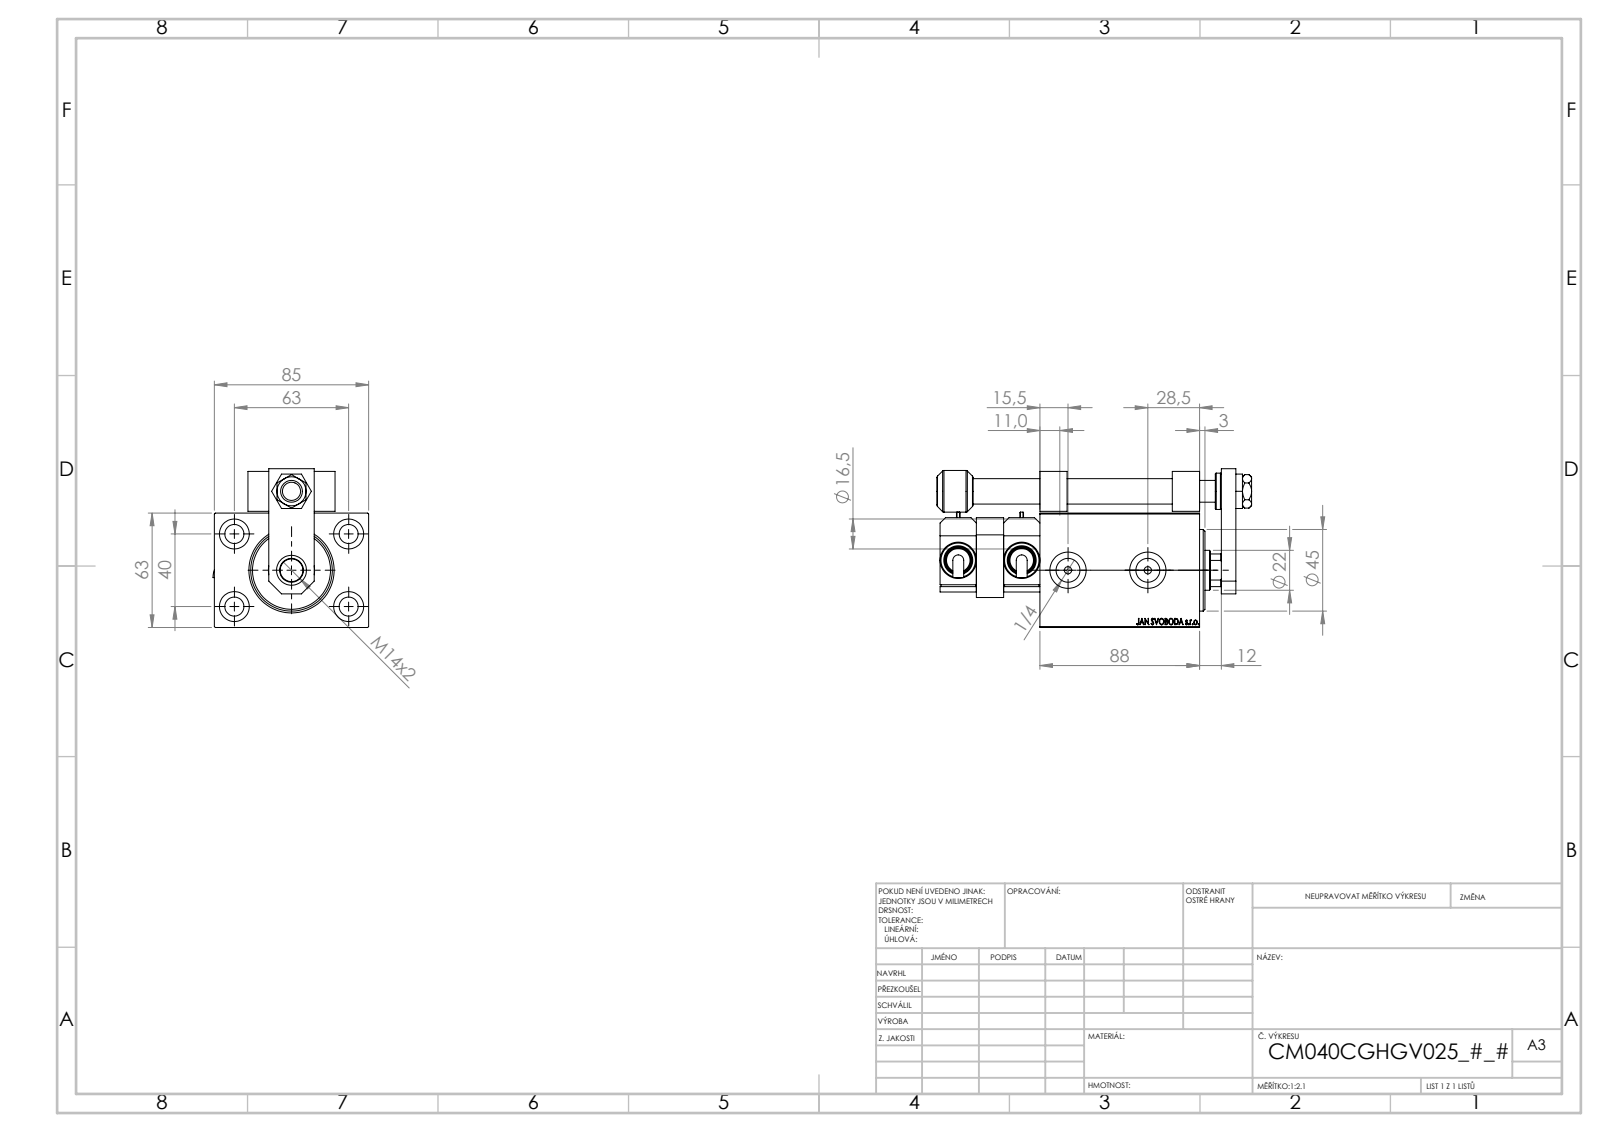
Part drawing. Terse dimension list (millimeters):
name: SWITCH DIM W_B; SWITCH_P_FRONT_BACK; NUT_D19_P; V450CM_VC_B (+7 more)
written by: SolidWorks 2019 (CONFIG_CONTROL_DESIGN)
unit: mm
bodies: 14 solids, 1087 faces (520 planar, 118 cylindrical, 449 other)
size: 173.5 × 87.5 × 85.76
volume: 566 079 mm³; area: 126 431 mm²
holes: 6× ⌀4, 5× ⌀16.5, 4× ⌀8, 4× ⌀10.5, 2× ⌀13.16, 2× ⌀20, 1× ⌀12, 1× ⌀12.5, 1× ⌀13, 1× ⌀14, 1× ⌀22, 1× ⌀25.5
bosses: 3× ⌀20, 2× ⌀16, 2× ⌀14, 2× ⌀6, 1× ⌀23
rounds: 1× R3, 1× R10.5
face distances: 63, 35, 20, 85, 108, 88, 15, 12, 76, 123
hole spacings: 37.31, 20, 39.3, 40, 63, 70.88, 73, 74.63
